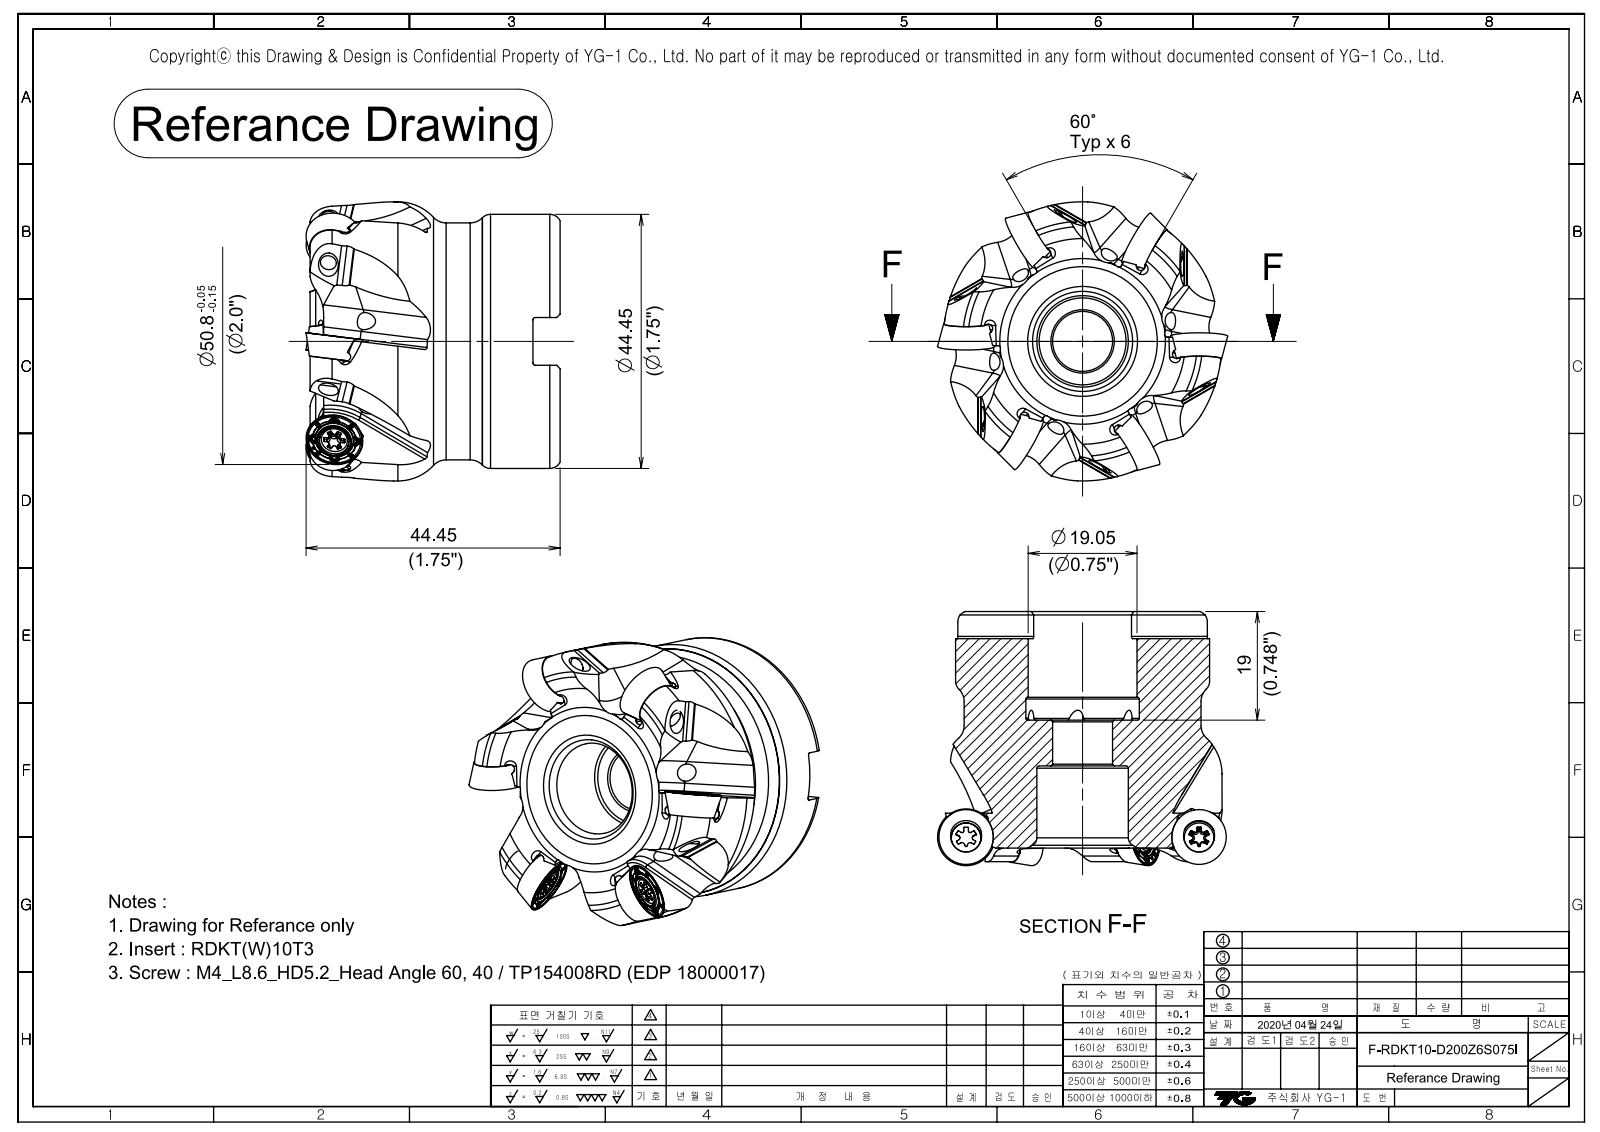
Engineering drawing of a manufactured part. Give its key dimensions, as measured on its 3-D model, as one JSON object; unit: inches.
{"part_name": "CUTTER-F-RDKT10-D200Z6S075I", "step_written_by": "SIEMENS PLM Software NX 10.0 (CONFIG_CONTROL_DESIGN)", "units": "inches", "bodies": {"solids": 13, "faces": 3505, "planar": 239, "cylindrical": 346, "other": 2920}, "overall_size": [1.999, 1.922, 1.75], "volume_in3": 3.105, "surface_area_in2": 23.98, "round_holes": [[0.118, 6], [0.138, 6], [0.173, 6], [0.413, 1], [0.63, 1], [0.75, 1], [0.781, 1]], "round_bosses_or_shafts": [[0.205, 6], [0.157, 6], [0.146, 6], [1.75, 1], [1.632, 1]], "partial_cylinders_radius": [[0.012, 108], [0.004, 72], [0.059, 24], [0.016, 20], [0.098, 6], [0.118, 6], [0.363, 6], [1.575, 6]], "face_to_face_distances": [1.629, 0.142, 1.442, 0.187, 0.881, 0.561, 0.748, 0.328, 0.566, 0.315]}
